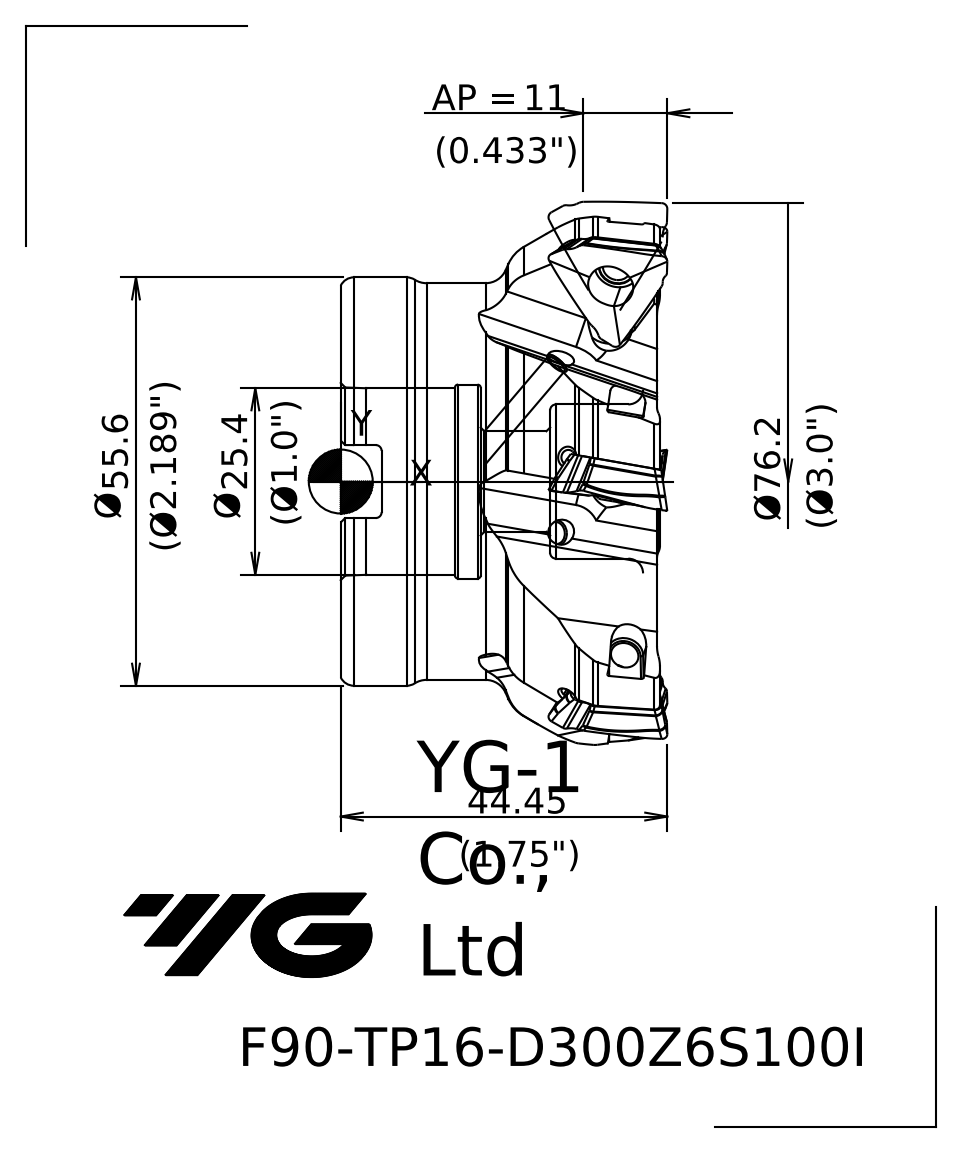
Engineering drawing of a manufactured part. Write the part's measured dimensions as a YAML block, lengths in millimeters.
part_name: "1022C79461C3qzgm"
step_written_by: "SIEMENS PLM Software NX 10.0 (AP203_CONFIGURATION_CONTROLLED_3D_DESIGN_OF_MECHANICAL_PARTS_AND_ASSEMBLIES_MIM_LF)"
units: millimeters
bodies: {solids: 1, faces: 77, planar: 18, cylindrical: 10, other: 49}
overall_size: [76.32, 76.32, 44.45]
volume: 113596
surface_area: 28360
round_holes:
  - {diameter: 13.7, count: 1}
  - {diameter: 21, count: 1}
  - {diameter: 25.4, count: 1}
  - {diameter: 26.4, count: 1}
round_bosses_or_shafts:
  - {diameter: 55.6, count: 1}
  - {diameter: 54, count: 1}
partial_cylinders:
  - {radius: 0.8, count: 2}
face_to_face_distances: [43.05, 24, 19.05, 37.49, 13.49, 5.56, 1.9, 22.1, 35.59, 41.15]
